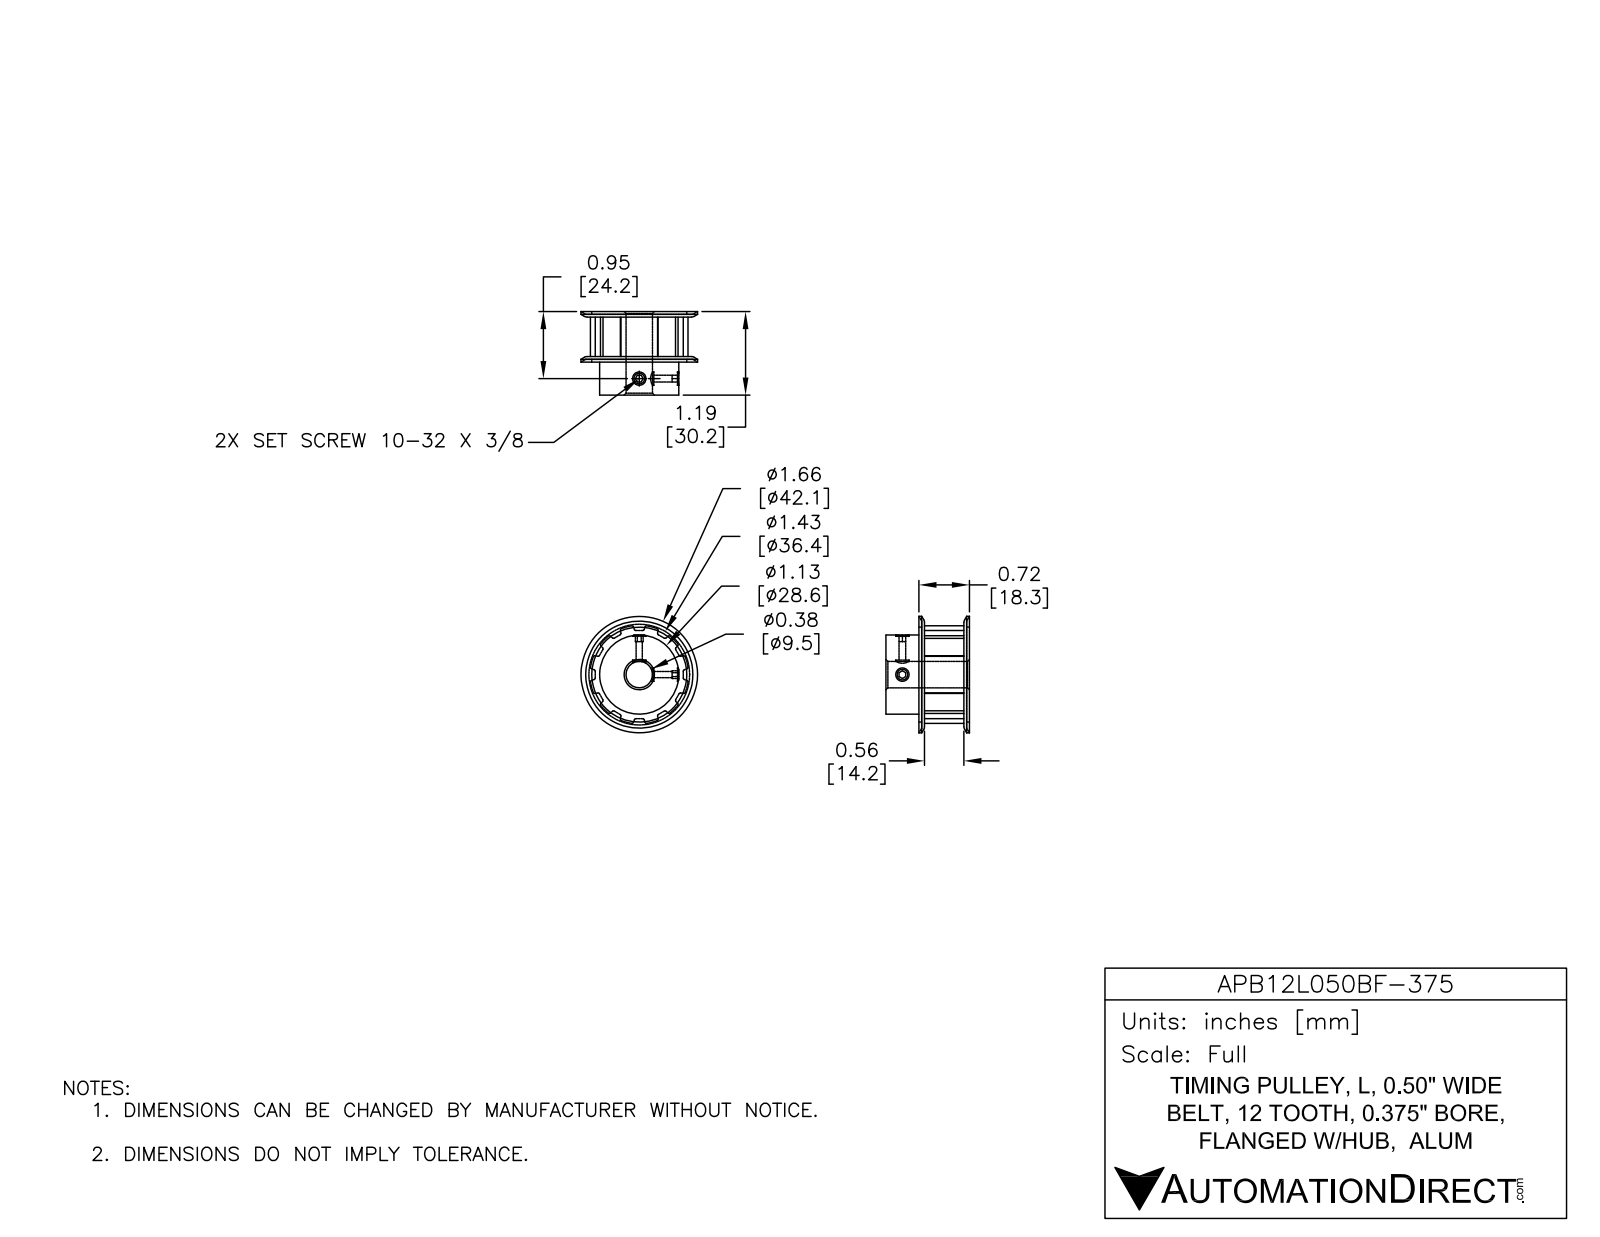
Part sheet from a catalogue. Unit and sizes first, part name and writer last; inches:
Units: inches
Overall size (bounding box): 1.656 × 1.656 × 1.188
Round holes (diameter × count): ⌀0.088 ×2, ⌀0.375 ×1
Round bosses / shafts (diameter × count): ⌀1.125 ×1
Partial cylindrical surfaces — rounded edges, fillets, slot ends (radius × count): R0.015 ×24, R0.646 ×1
Main face-to-face distances: 1.402, 1.188, 0.68, 0.508, 0.04, 0.64, 1.148, 0.504, 0.04, 0.6
Volume: 1.425 in³ · Surface area: 12.23 in²
Bodies: 1 solid, 114 faces (42 planar, 50 cylindrical, 22 other)
Part name (STEP PRODUCT): APB12L050BF-375
STEP written by: SolidWorks 2014 (AUTOMOTIVE_DESIGN)
